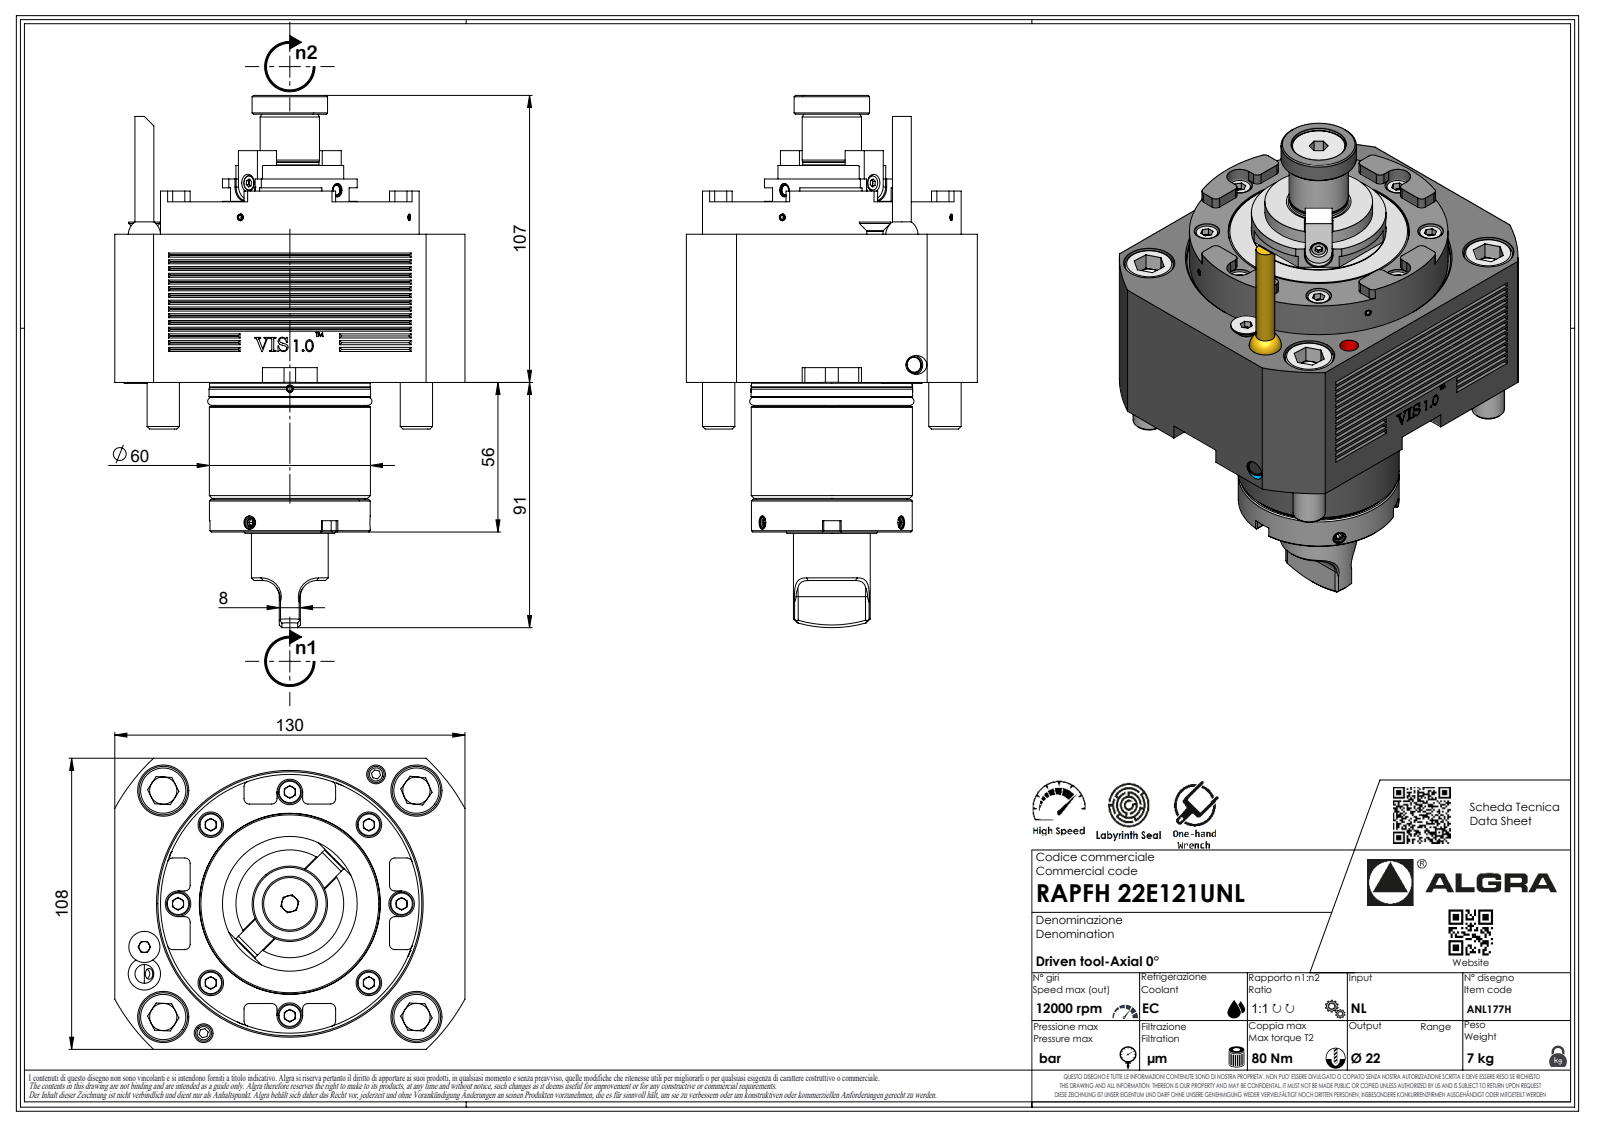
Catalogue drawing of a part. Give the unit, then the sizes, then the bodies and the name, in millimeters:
Units: millimetres
Overall size (bounding box): 197.5 × 130 × 108
Round holes (diameter × count): ⌀2.1 ×1, ⌀4 ×1
Round bosses / shafts (diameter × count): ⌀12 ×4, ⌀96 ×1, ⌀60 ×1, ⌀50 ×1, ⌀40 ×1, ⌀28.5 ×1, ⌀28 ×1, ⌀22 ×1
Partial cylindrical surfaces — rounded edges, fillets, slot ends (radius × count): R2 ×25, R8 ×8, R0.33 ×7, R0.52 ×7, R3.7 ×7, R6 ×6, R4.75 ×4, R5 ×3
Main face-to-face distances: 55, 108, 12, 67, 130, 55.5, 110.5, 122.5, 61.5, 5.5
Volume: 1 044 000 mm³ · Surface area: 79 722 mm²
Bodies: 1 solid, 513 faces (342 planar, 94 cylindrical, 77 other)
Part name (STEP PRODUCT): RAPFH22E121UNL
STEP written by: SolidWorks 2023 (AUTOMOTIVE_DESIGN)
